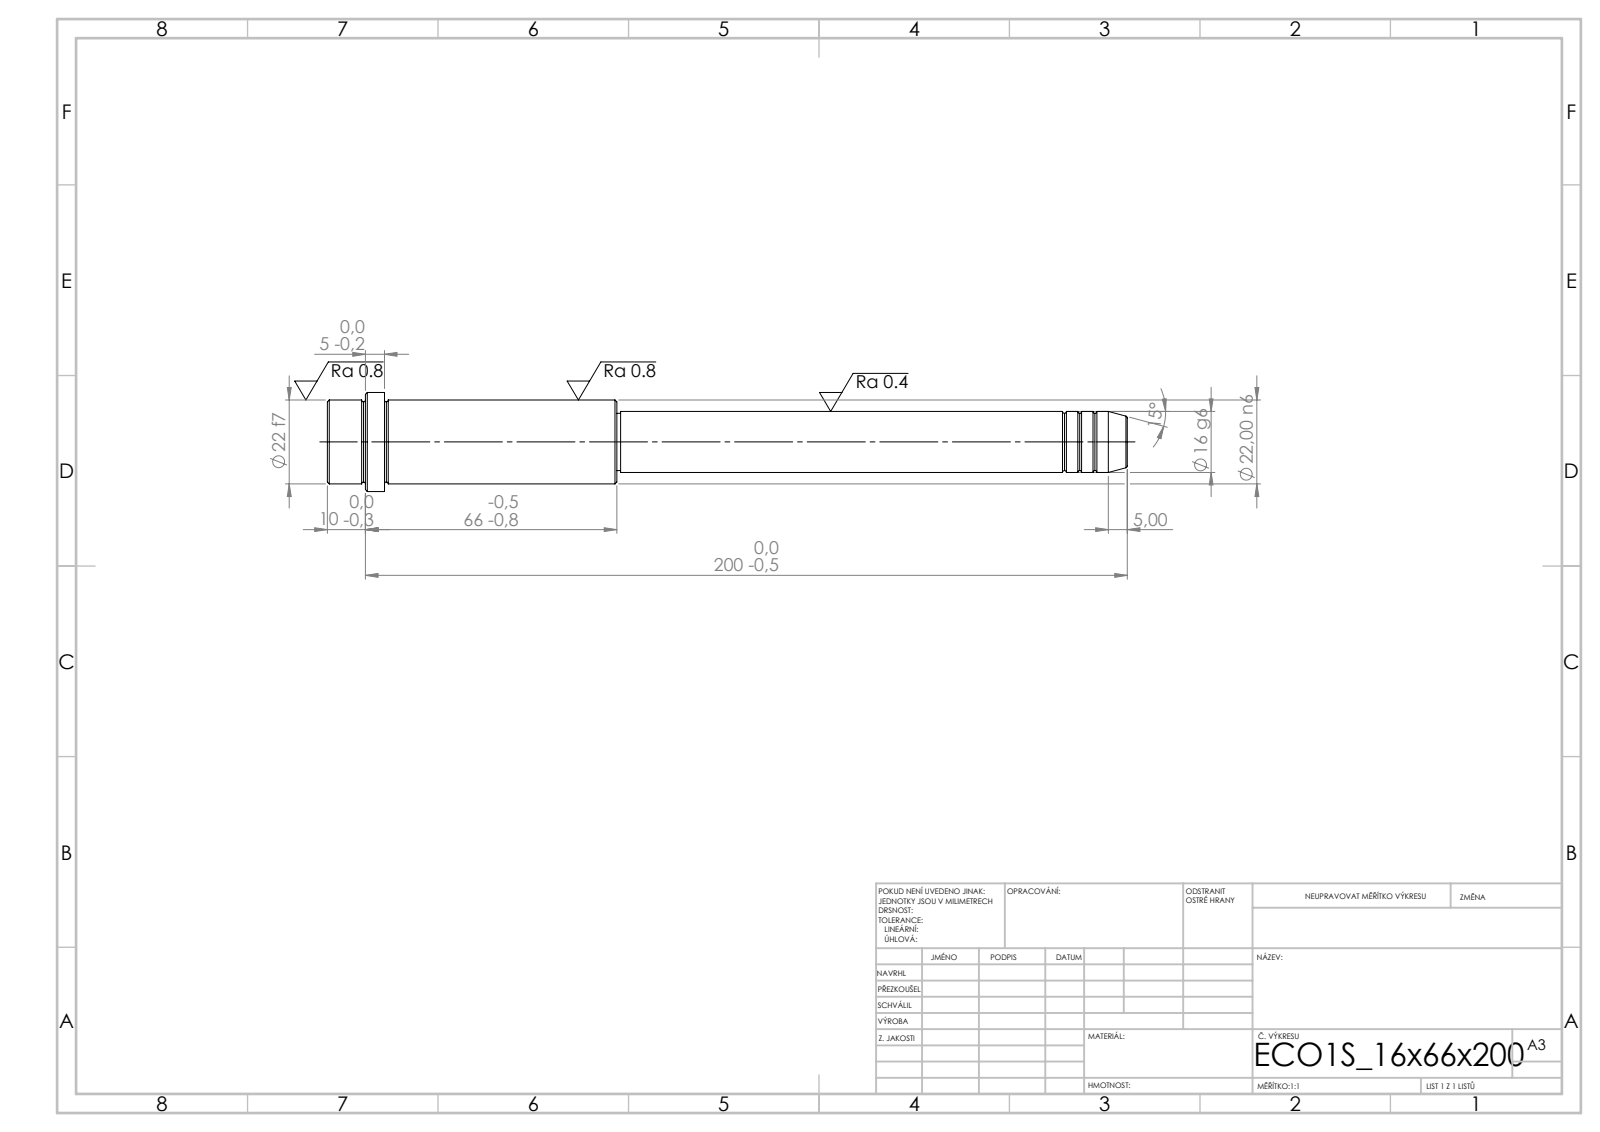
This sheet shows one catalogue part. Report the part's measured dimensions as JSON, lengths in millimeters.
{"step_written_by": "SolidWorks 2019 (CONFIG_CONTROL_DESIGN)", "units": "millimeters", "bodies": {"solids": 1, "faces": 52, "planar": 6, "cylindrical": 16, "other": 30}, "overall_size": [210, 26, 26], "volume_mm3": 56264, "surface_area_mm2": 13163, "round_bosses_or_shafts": [[26, 1], [22, 1], [16, 1], [15, 1]], "face_to_face_distances": [76, 61, 15, 134, 195, 210, 200, 66, 5, 10]}
